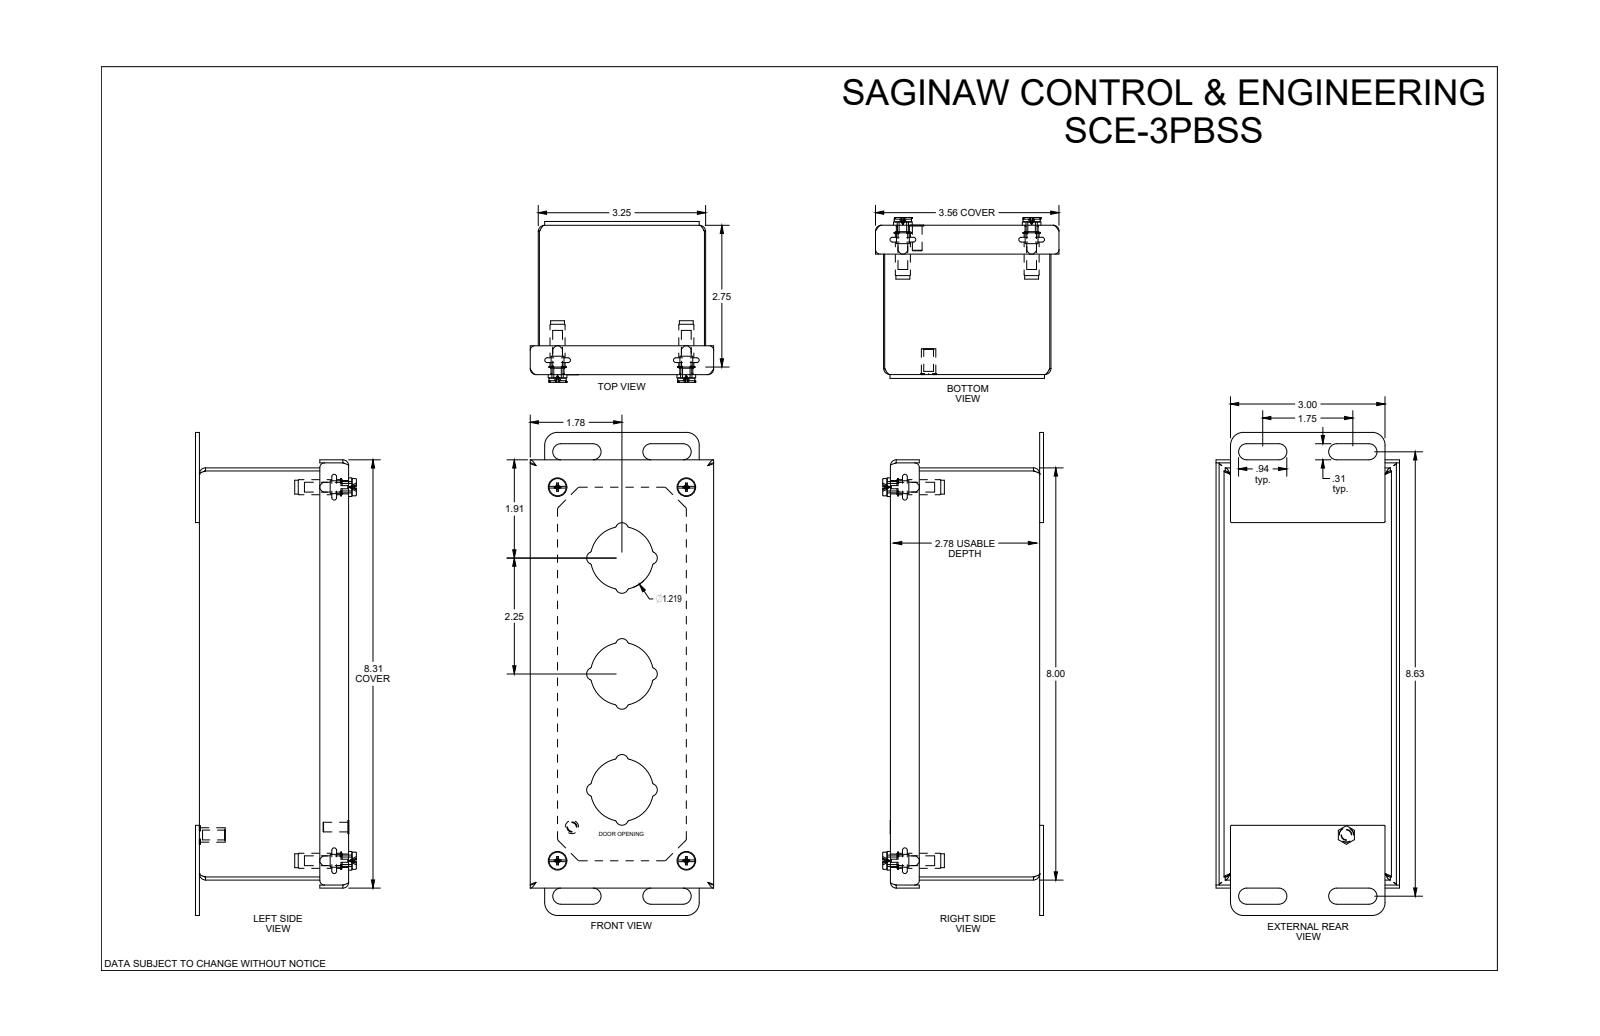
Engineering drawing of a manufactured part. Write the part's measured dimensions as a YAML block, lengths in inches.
part_name: "SCE-3PB"
step_written_by: "SolidWorks 2021 (AUTOMOTIVE_DESIGN)"
units: inches
bodies: {solids: 14, faces: 482, planar: 159, cylindrical: 170, other: 153}
overall_size: [9.375, 3.563, 3.124]
volume: 8.933
surface_area: 296
round_holes:
  - {diameter: 0.22, count: 4}
  - {diameter: 0.266, count: 4}
  - {diameter: 0.34, count: 4}
round_bosses_or_shafts:
  - {diameter: 0.188, count: 5}
  - {diameter: 0.362, count: 4}
  - {diameter: 0.334, count: 4}
  - {diameter: 0.26, count: 4}
  - {diameter: 0.146, count: 4}
  - {diameter: 0.256, count: 1}
partial_cylinders:
  - {radius: 0.04, count: 44}
  - {radius: 0.1, count: 20}
  - {radius: 0.125, count: 12}
  - {radius: 0.015, count: 8}
  - {radius: 0.06, count: 8}
  - {radius: 0.115, count: 8}
  - {radius: 0.156, count: 8}
  - {radius: 0.245, count: 8}
face_to_face_distances: [0.06, 2.838, 0.06, 2.778, 2.898, 3.19, 3.25, 3.13, 3.19, 2.69]
hole_center_spacings: [2.5, 7.25, 7.669]
